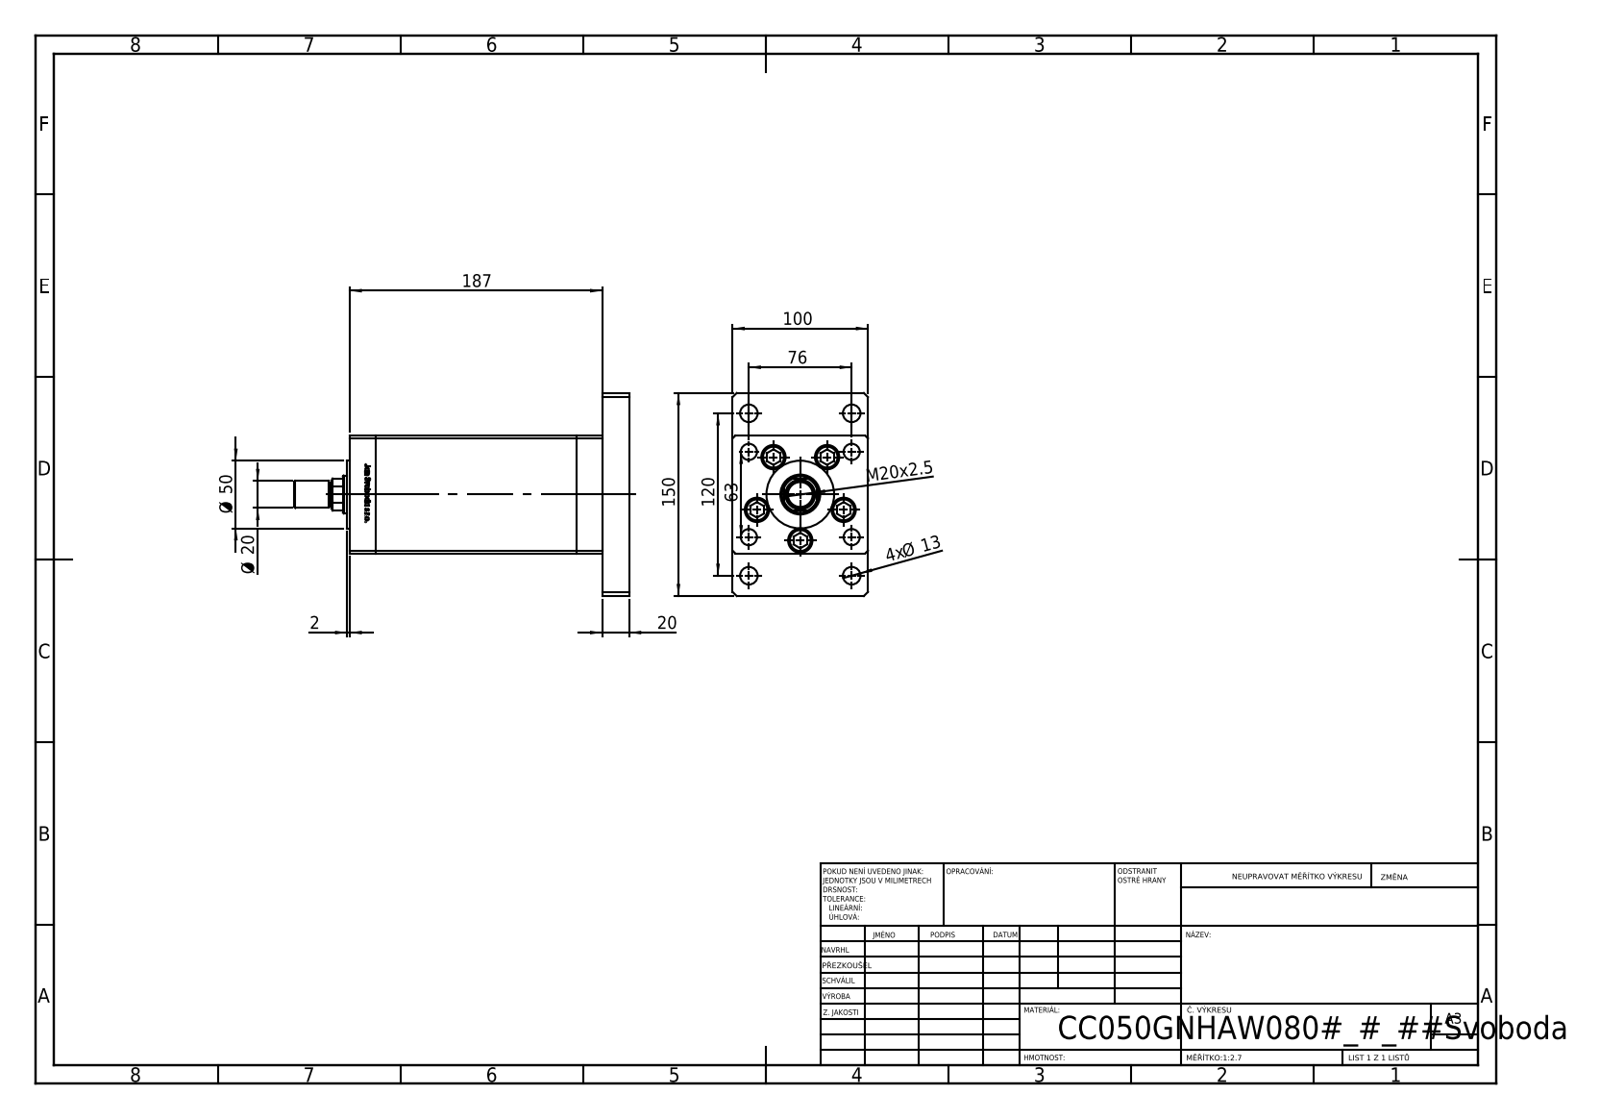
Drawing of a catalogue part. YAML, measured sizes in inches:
part_name: "V220C_G_MIDDLE; V220C_FRONT_G; ALLEN BOLT; V220CC_MALE_METRIC (+3 more)"
step_written_by: "SolidWorks 2019 (CONFIG_CONTROL_DESIGN)"
units: inches
bodies: {solids: 20, faces: 1322, planar: 519, cylindrical: 191, other: 612}
overall_size: [9.744, 5.906, 3.937]
volume: 104.1
surface_area: 401.7
round_holes:
  - {diameter: 0.472, count: 9}
  - {diameter: 0.531, count: 5}
  - {diameter: 0.709, count: 5}
  - {diameter: 0.512, count: 4}
  - {diameter: 0.669, count: 4}
  - {diameter: 0.079, count: 2}
  - {diameter: 0.518, count: 2}
  - {diameter: 0.728, count: 1}
  - {diameter: 1.102, count: 1}
  - {diameter: 1.161, count: 1}
  - {diameter: 2.677, count: 1}
round_bosses_or_shafts:
  - {diameter: 0.315, count: 9}
  - {diameter: 0.669, count: 5}
  - {diameter: 1.969, count: 1}
  - {diameter: 0.787, count: 1}
  - {diameter: 0.709, count: 1}
partial_cylinders:
  - {radius: 0.037, count: 2}
  - {radius: 0.531, count: 1}
face_to_face_distances: [0.748, 3.937, 6.594, 3.425, 5.846, 0.787, 7.382, 1.535, 8.13, 7.343]
hole_center_spacings: [1.339, 1.122, 1.943, 2.796, 2.992, 3.196, 3.602, 4.683]
